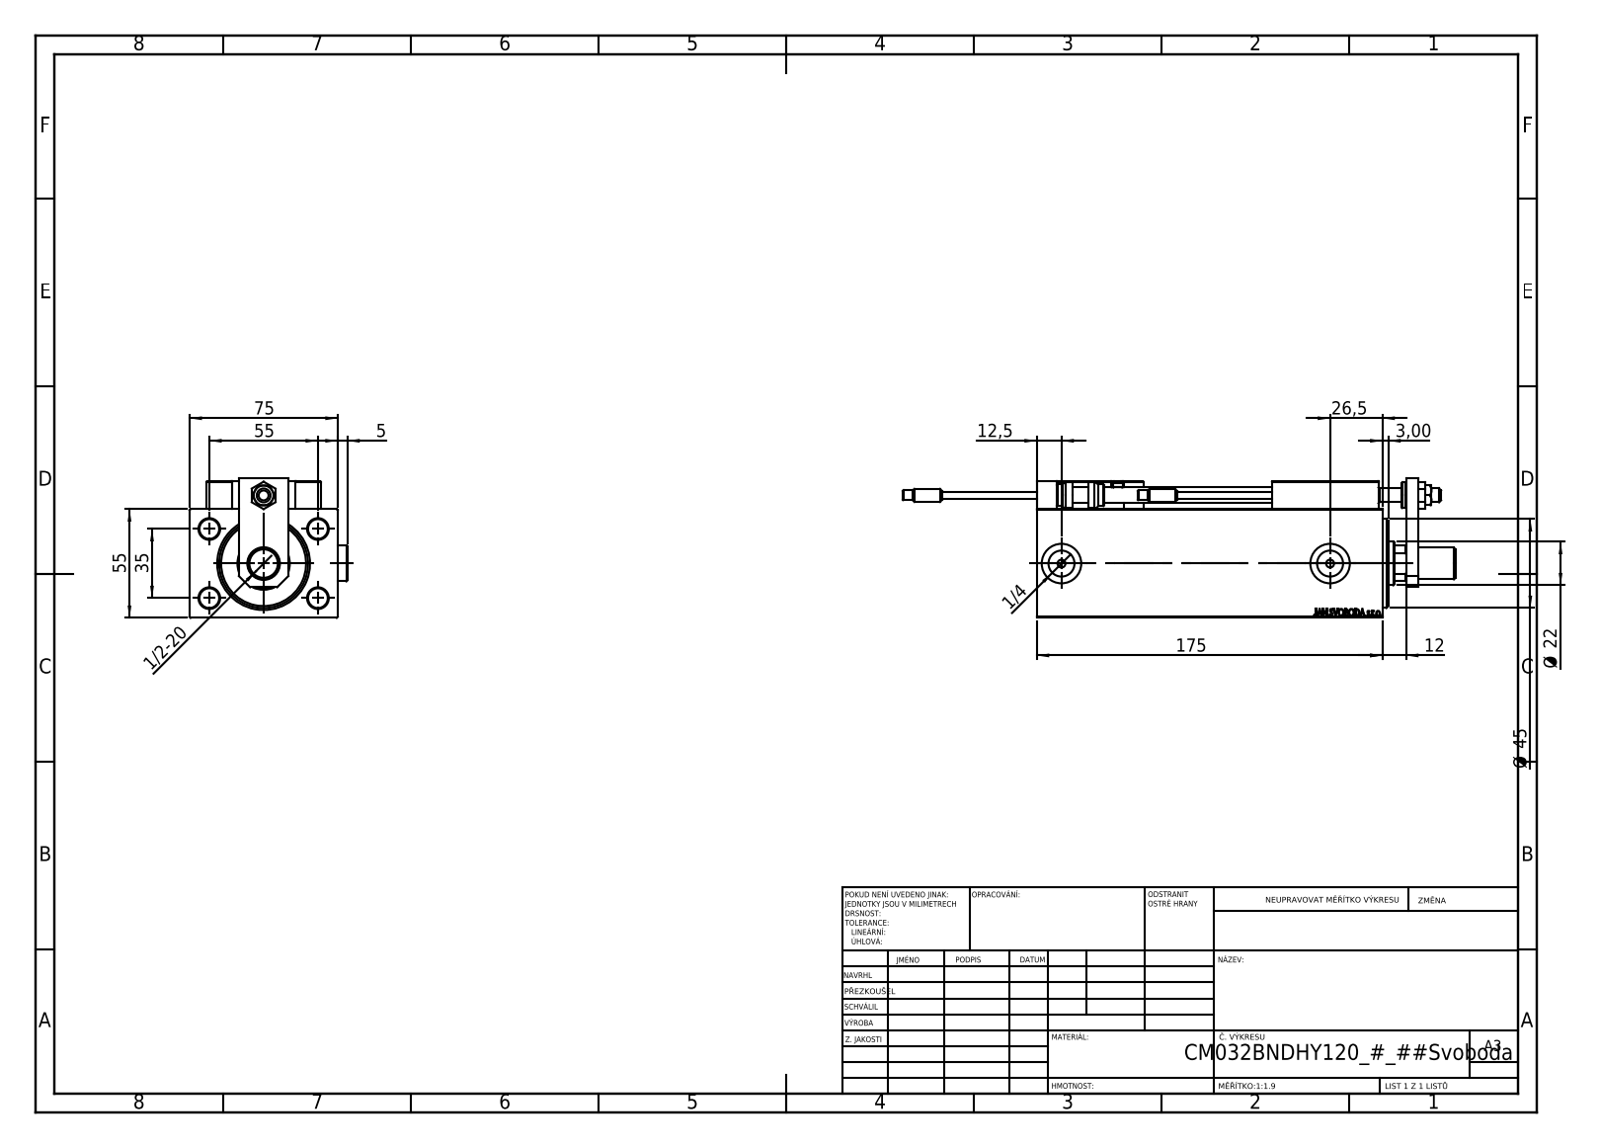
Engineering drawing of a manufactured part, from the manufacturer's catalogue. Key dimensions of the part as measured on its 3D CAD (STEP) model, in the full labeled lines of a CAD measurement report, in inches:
Part name (STEP PRODUCT): MAGNET; SWITCH_X_FRONT_BACK; KONCOVKA_Y; NUT_D12 (+7 more)
STEP written by: SolidWorks 2019 (CONFIG_CONTROL_DESIGN)
Units: inches
Bodies: 27 solids, 1407 faces (600 planar, 212 cylindrical, 595 other)
Overall size (bounding box): 11.024 × 3.146 × 2.776
Volume: 43.75 in³ · Surface area: 201 in²
Round holes (diameter × count): ⌀0.157 ×6, ⌀0.315 ×5, ⌀0.126 ×4, ⌀0.394 ×4, ⌀0.197 ×2, ⌀0.518 ×2, ⌀0.787 ×2, ⌀0.276 ×1, ⌀0.413 ×1, ⌀0.65 ×1, ⌀0.866 ×1, ⌀1.004 ×1
Round bosses / shafts (diameter × count): ⌀0.197 ×4, ⌀0.709 ×2, ⌀0.256 ×2, ⌀0.15 ×2, ⌀0.63 ×1, ⌀0.551 ×1, ⌀0.512 ×1, ⌀0.433 ×1
Partial cylindrical surfaces — rounded edges, fillets, slot ends (radius × count): R0.012 ×30, R0.118 ×2, R0.413 ×1
Main face-to-face distances: 2.165, 2.953, 0.394, 0.472, 0.551, 0.197, 0.276, 2.717, 0.984, 6.89
Hole centre spacings: 1.283, 0.448, 0.787, 1.165, 1.169, 1.273, 1.378, 1.42
